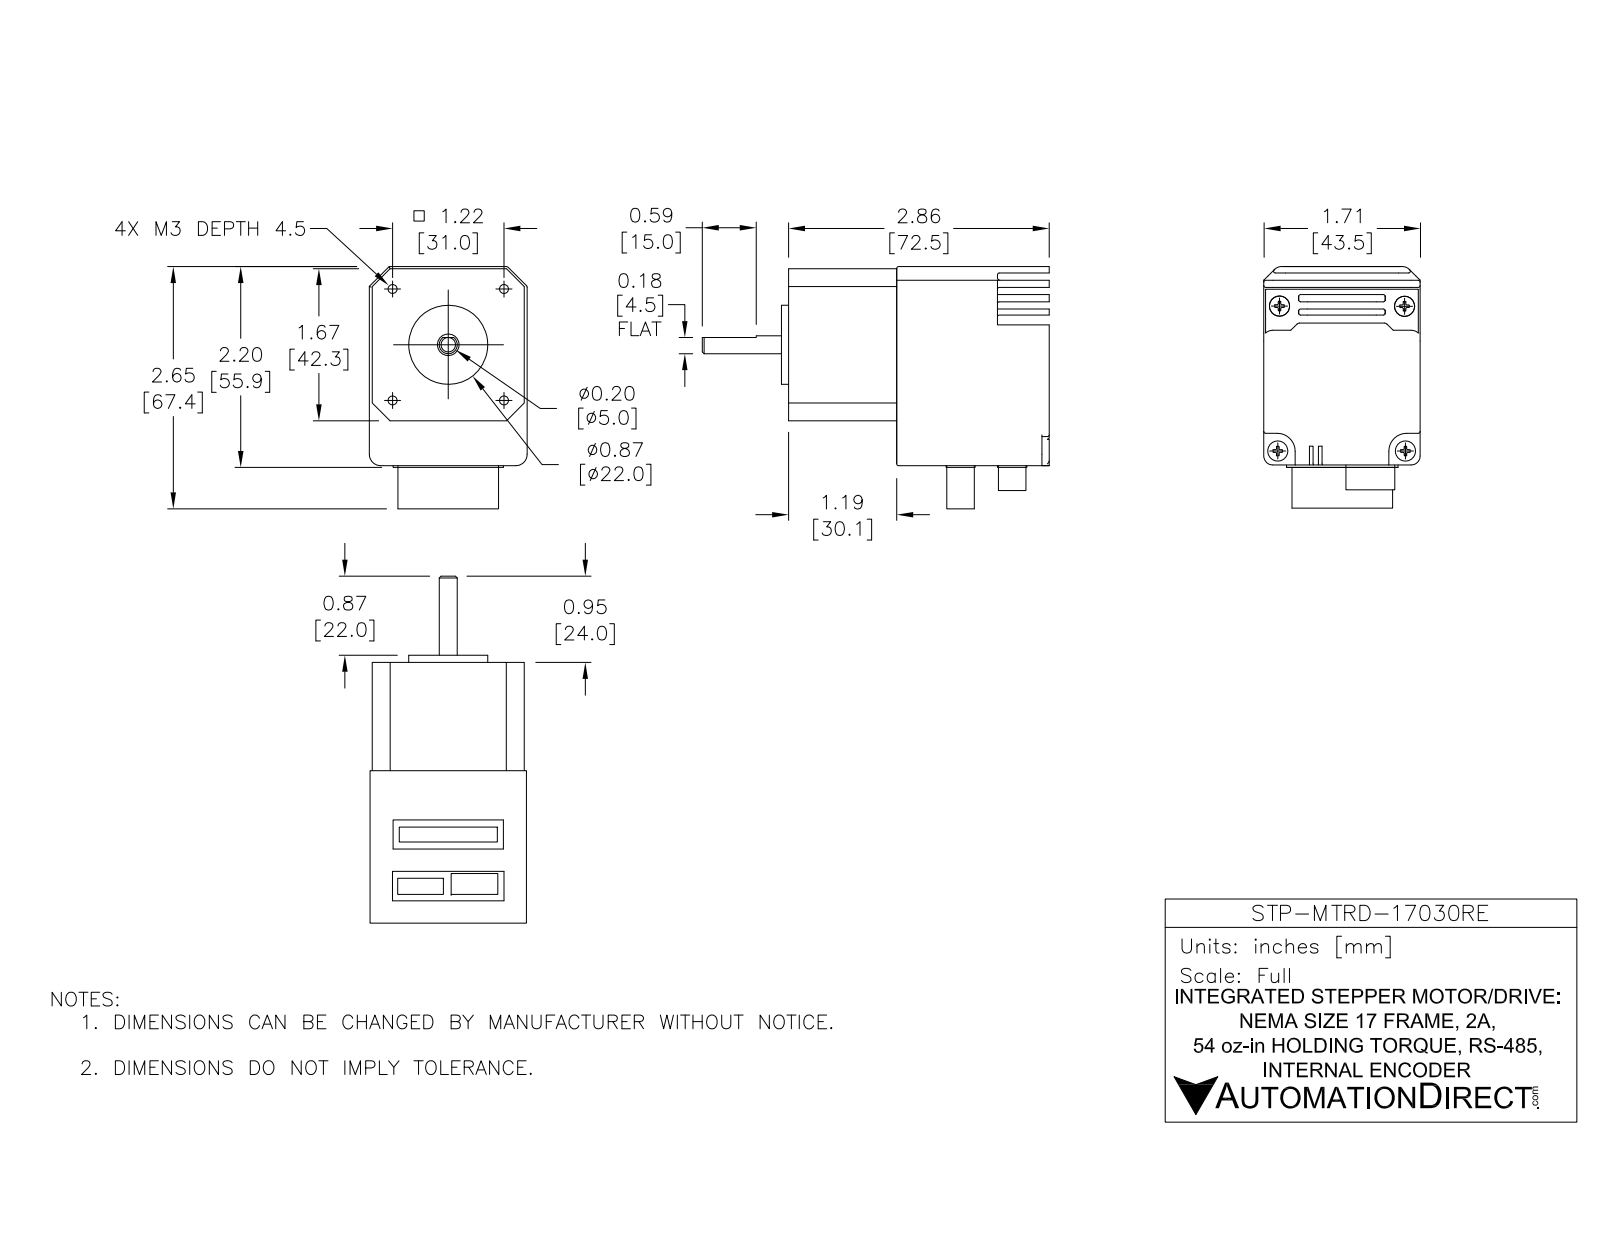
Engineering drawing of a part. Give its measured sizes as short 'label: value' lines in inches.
name: STP-MTRD-17030RE
written by: SolidWorks 2017 (AUTOMOTIVE_DESIGN)
unit: in
bodies: 2 solids, 397 faces (149 planar, 157 cylindrical, 91 other)
size: 3.799 × 2.199 × 1.713
volume: 8.69 in³; area: 35.8 in²
holes: 4× ⌀0.118, 1× ⌀0.295, 1× ⌀0.591
bosses: 4× ⌀0.22, 1× ⌀0.866, 1× ⌀0.197
rounds: 75× R0.02, 12× R0.098, 4× R0.027, 4× R0.431, 4× R0.999, 2× R0.197, 1× R0.03
face distances: 0.079, 0.071, 1.642, 1.713, 1.571, 2.854, 0.157, 1.618, 0.047, 2.173
hole spacings: 0.863, 1.22, 1.726
